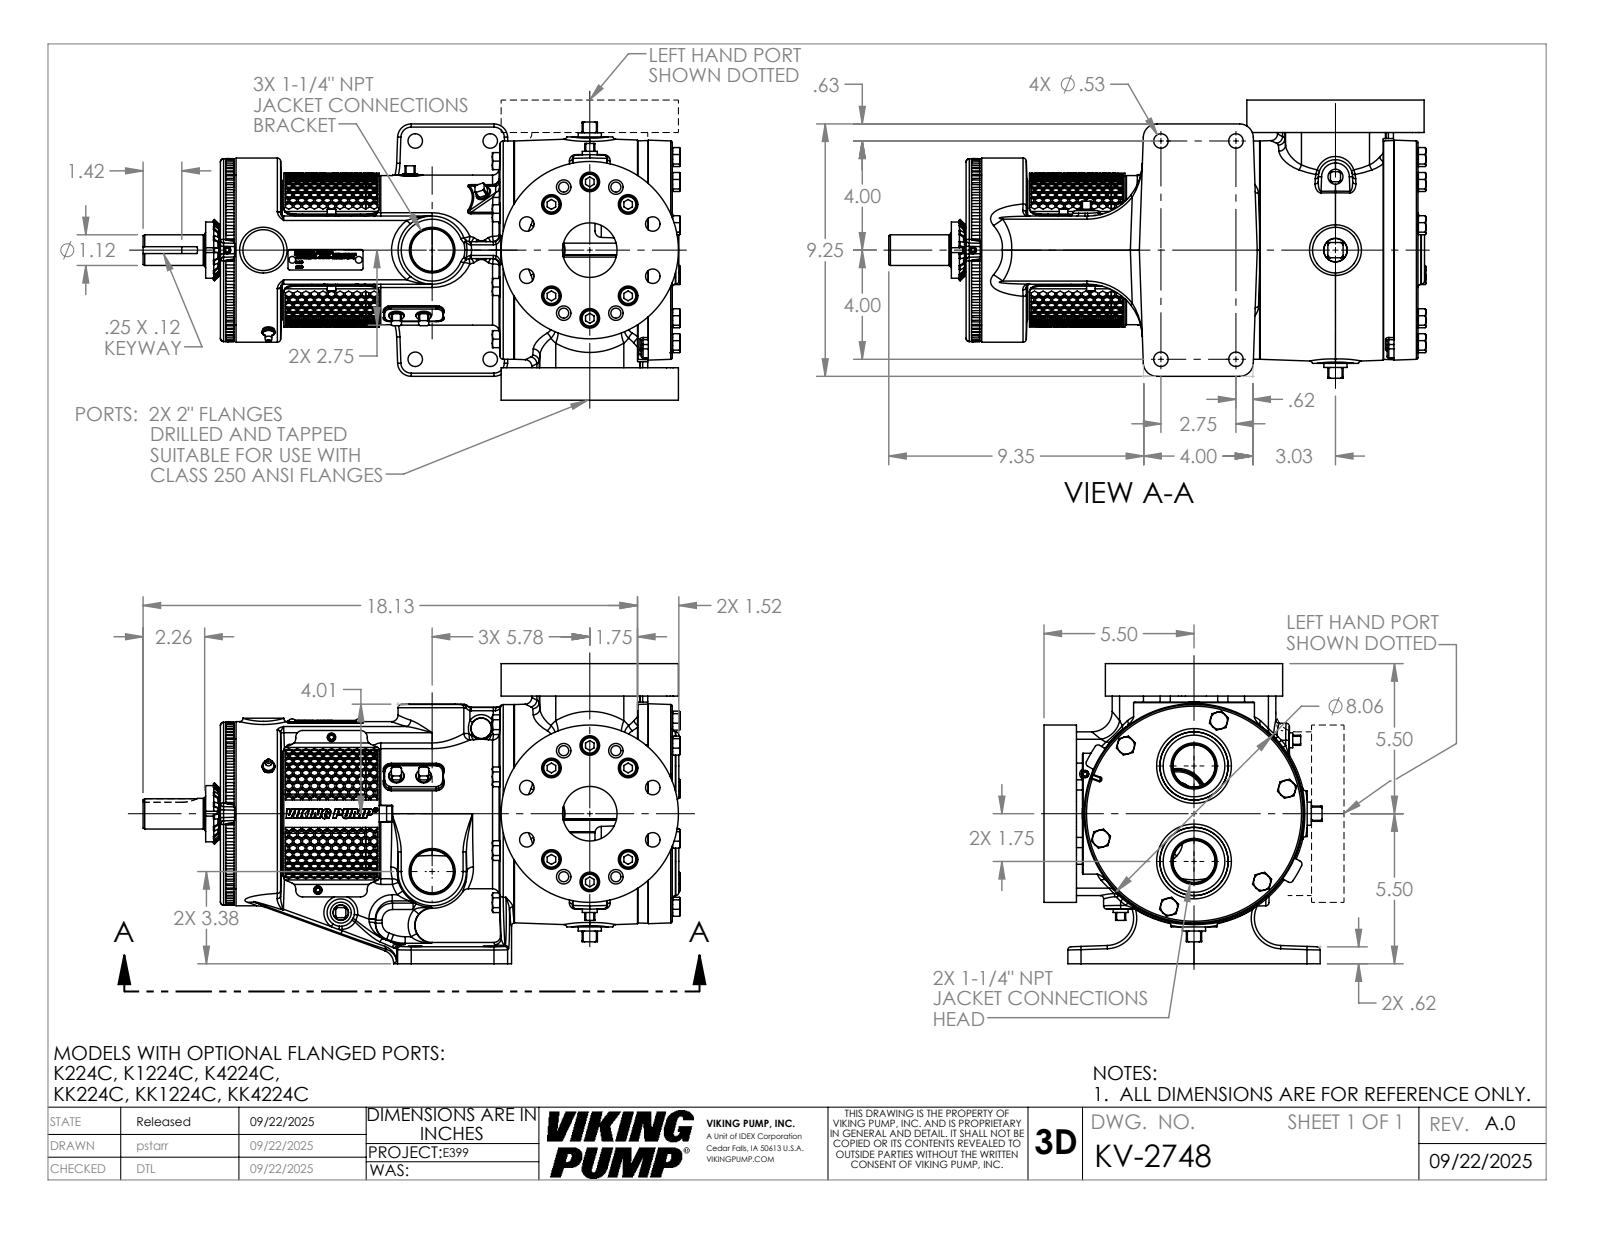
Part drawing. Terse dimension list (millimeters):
name: KV-2748
written by: SolidWorks 2024 (AUTOMOTIVE_DESIGN)
unit: mm
bodies: 1 solid, 4114 faces (1408 planar, 565 cylindrical, 2141 other)
size: 500.3 × 279.4 × 259
volume: 11 180 000 mm³; area: 714 800 mm²
holes: 16× ⌀13.5, 12× ⌀18.3, 9× ⌀6.4, 8× ⌀9.3, 8× ⌀19.8, 6× ⌀5, 4× ⌀13.5, 2× ⌀4, 2× ⌀8, 2× ⌀50.8, 1× ⌀6.5, 1× ⌀11.5
bosses: 23× ⌀15.9, 3× ⌀15.9, 3× ⌀7.9, 3× ⌀4.8, 2× ⌀165.1, 1× ⌀203.2, 1× ⌀171.5, 1× ⌀139.7
rounds: 42× R3, 22× R6.1, 20× R0.8, 18× R25.4, 16× R3, 9× R1.5, 8× R6.4, 8× R12.7
face distances: 279.4, 30.2, 285.6, 135.2, 420.9, 12.7, 14.6, 120.7, 406.3, 249.2
hole spacings: 63.5, 76.2, 26.2, 48.6, 24.8, 29.3, 35, 55.5
